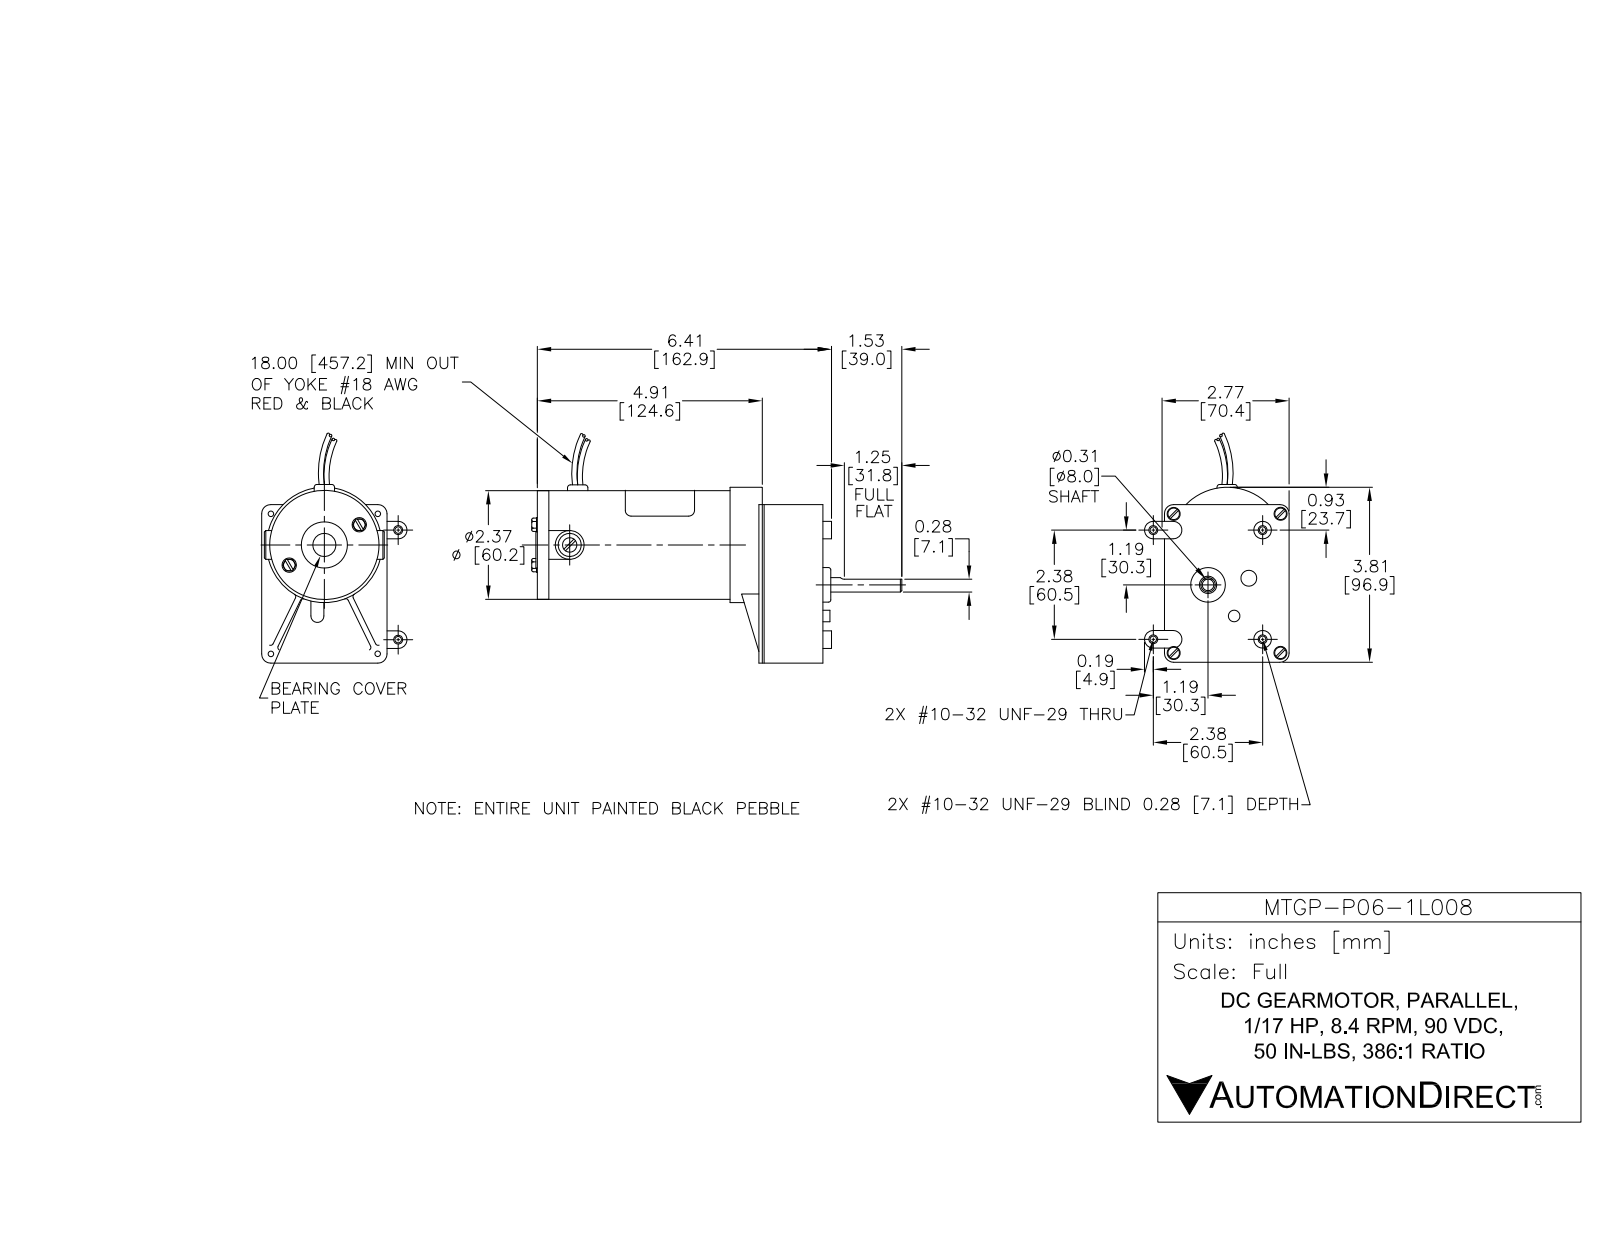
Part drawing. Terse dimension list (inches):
name: MTGP-P06-1L008
written by: SolidWorks 2015 (AUTOMOTIVE_DESIGN)
unit: in
bodies: 27 solids, 270 faces (117 planar, 132 cylindrical, 21 other)
size: 7.922 × 5.092 × 3.181
volume: 20.18 in³; area: 156.4 in²
holes: 6× ⌀0.194, 4× ⌀0.063, 4× ⌀0.283, 2× ⌀0.156, 1× ⌀0.25, 1× ⌀0.312, 1× ⌀0.562, 1× ⌀1, 1× ⌀2.25
bosses: 4× ⌀0.312, 2× ⌀0.38, 2× ⌀0.1, 1× ⌀2.46, 1× ⌀2.375, 1× ⌀0.75, 1× ⌀0.625, 1× ⌀0.625
rounds: 10× R0.031, 4× R0.1, 4× R0.19, 2× R0.25, 1× R0.134, 1× R0.141, 1× R1.222
face distances: 1.4, 0.25, 4.833, 6.233, 4.583, 5.983, 4.194, 3.944, 0.639, 2.039
hole spacings: 1.223, 1.729, 2.411, 2.38, 0.373, 0.44, 0.875, 1.306
